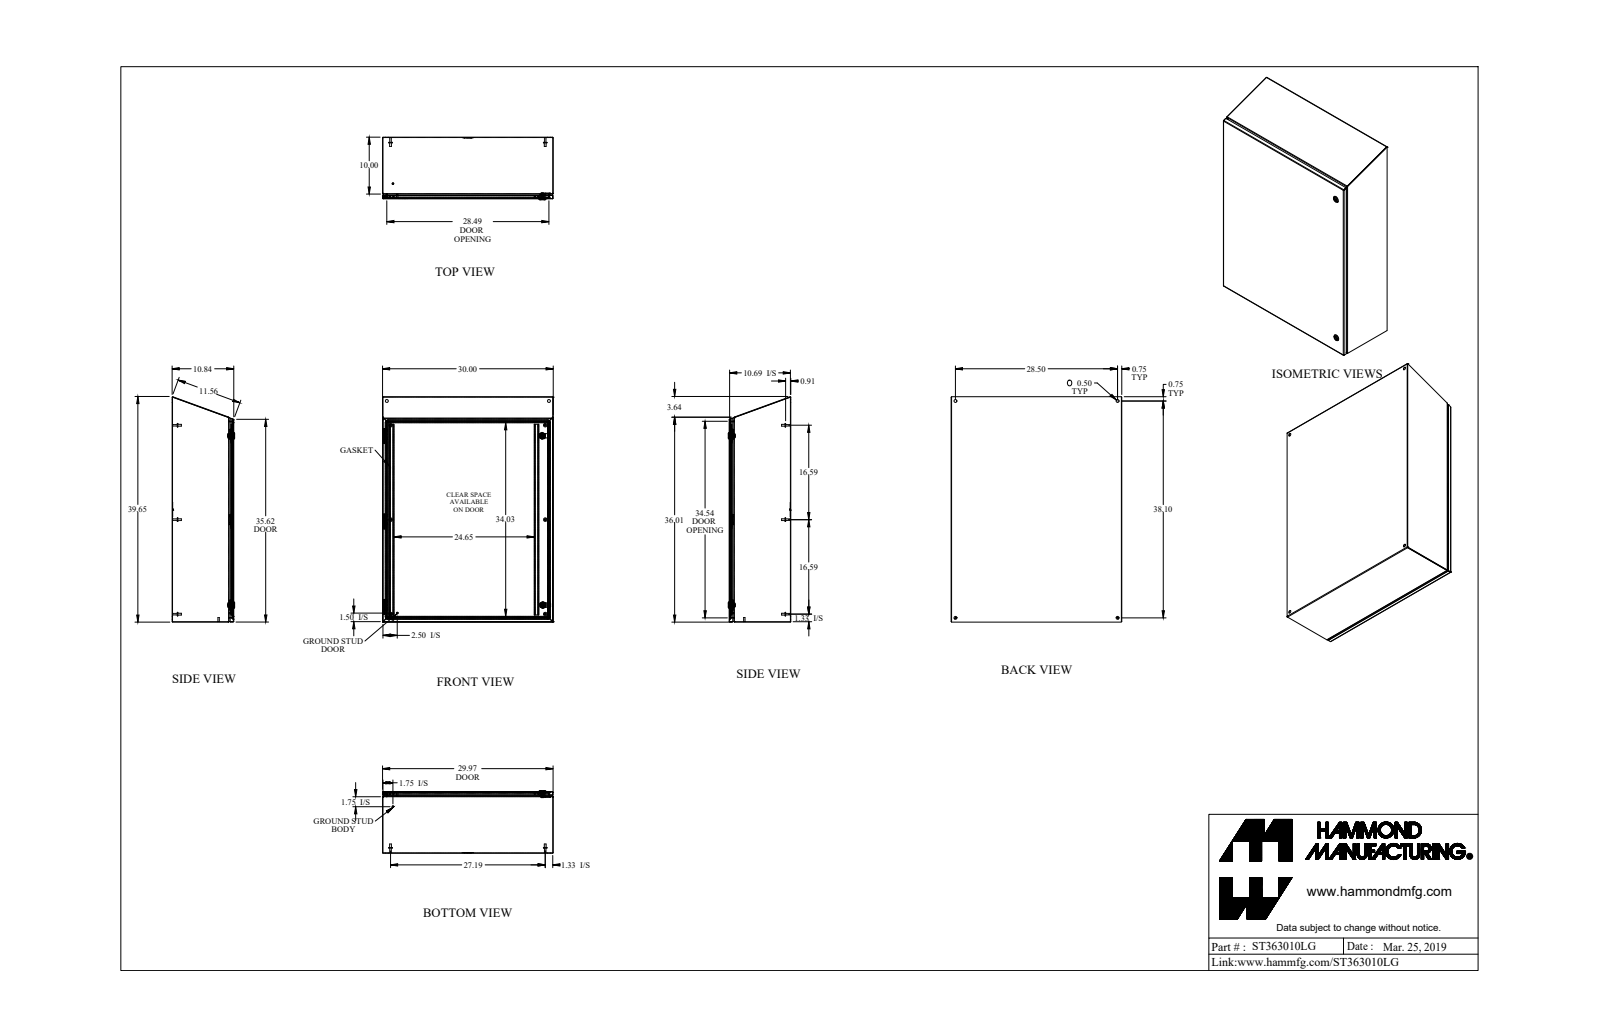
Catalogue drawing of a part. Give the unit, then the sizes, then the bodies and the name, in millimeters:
Units: millimetres
Overall size (bounding box): 1005.8 × 762 × 279.3
Round holes (diameter × count): ⌀12.7 ×4, ⌀4.4 ×2, ⌀5.9 ×2, ⌀15.9 ×2, ⌀19.9 ×2, ⌀6.1 ×1, ⌀6.1 ×1
Round bosses / shafts (diameter × count): ⌀15.9 ×6, ⌀8 ×6, ⌀6.9 ×6, ⌀27.9 ×2, ⌀13.3 ×2, ⌀7.4 ×2, ⌀7.1 ×2, ⌀6.4 ×2
Partial cylindrical surfaces — rounded edges, fillets, slot ends (radius × count): R0.9 ×18, R2.7 ×18, R1.1 ×12, R2.1 ×12, R0.2 ×6, R1.6 ×6, R4.8 ×5, R3.2 ×4
Main face-to-face distances: 1.8, 273.4, 271.6, 1.8, 275.3, 273.4, 760.2, 758.3, 762, 21.3
Hole centre spacings: 723.9, 967.7, 1208.5, 63.3, 158.2, 699, 710.4, 755.4
Volume: 4 872 000 mm³ · Surface area: 5 379 000 mm²
Bodies: 35 solids, 900 faces (438 planar, 290 cylindrical, 172 other)
Part name (STEP PRODUCT): ST363010LG
STEP written by: SolidWorks 2018 (AUTOMOTIVE_DESIGN)
